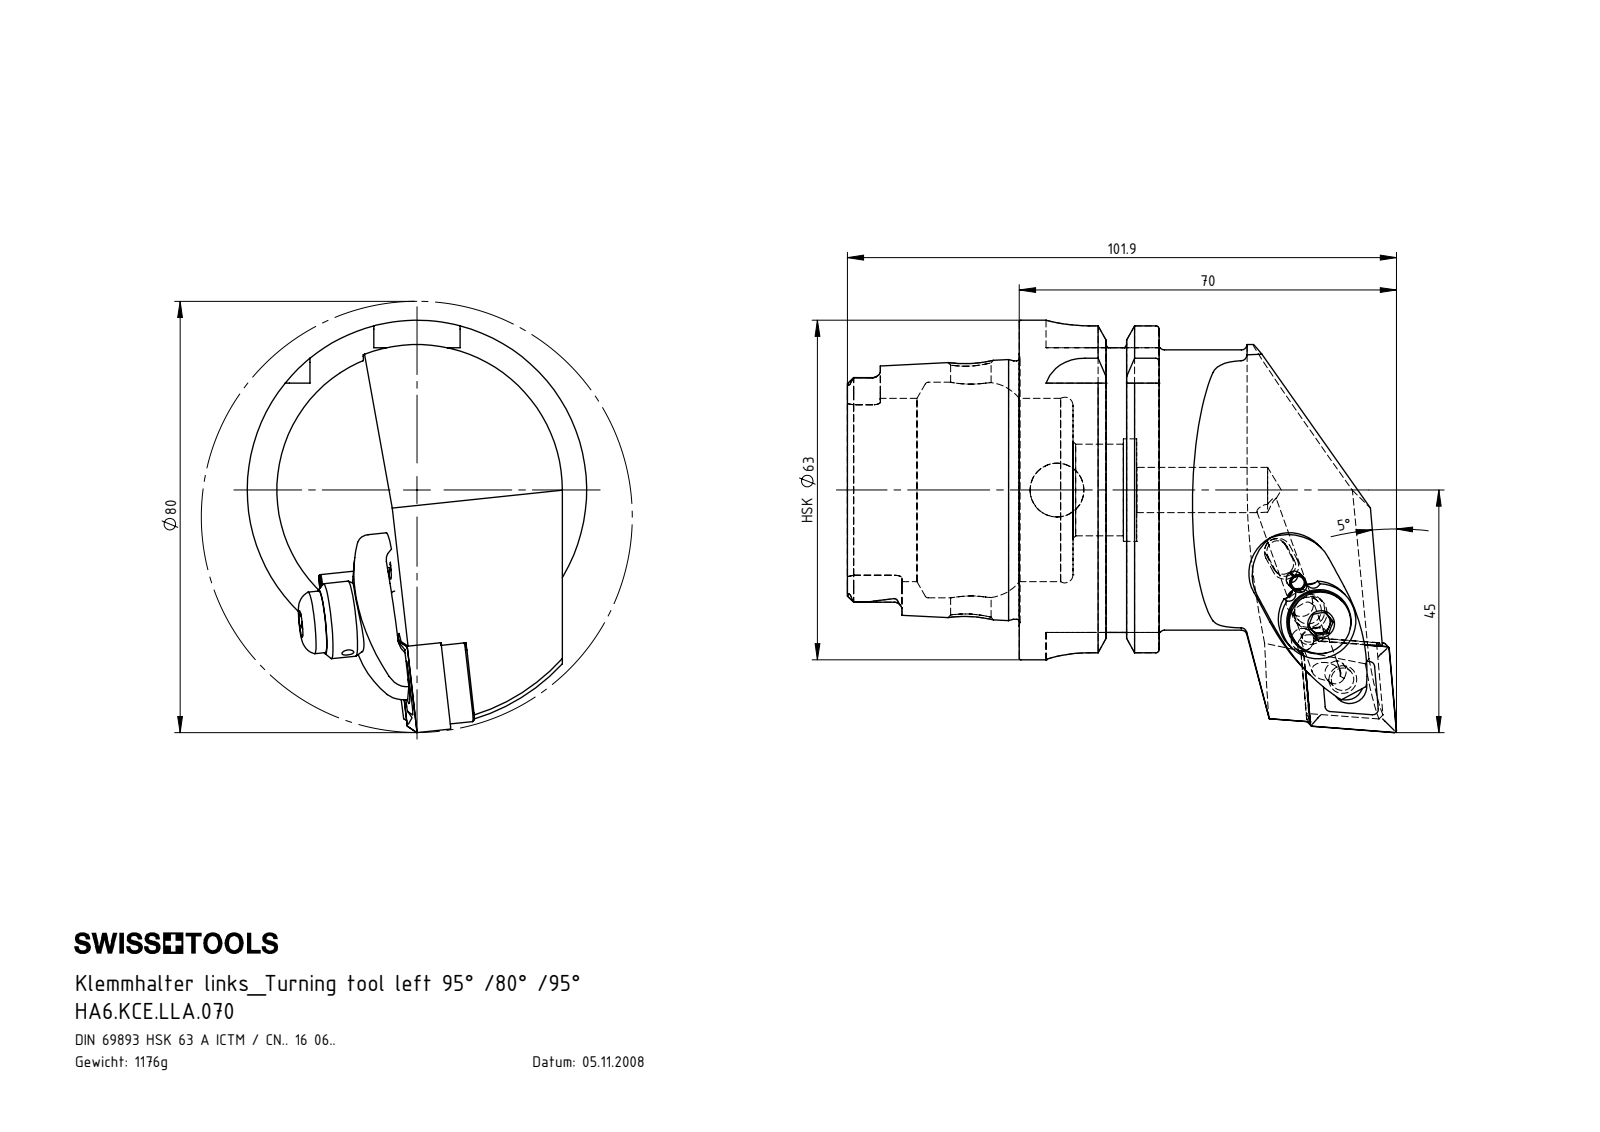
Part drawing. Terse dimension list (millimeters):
name: ISO 13337 - 3 x 12_PreviewCfg; HA6-KCE.LLA.070_C; WCC-ER5.102.012_B; WCE-ER2.001.012_A (+7 more)
written by: SolidWorks 2017 (AUTOMOTIVE_DESIGN)
unit: mm
bodies: 12 solids, 464 faces (125 planar, 150 cylindrical, 189 other)
size: 101.9 × 76.5 × 63
volume: 148 539 mm³; area: 36 454 mm²
holes: 3× ⌀2, 3× ⌀5, 2× ⌀4.2, 1× ⌀2.4, 1× ⌀3, 1× ⌀6, 1× ⌀6.2, 1× ⌀6.35, 1× ⌀7, 1× ⌀7.5, 1× ⌀7.9, 1× ⌀8.4
bosses: 2× ⌀6, 2× ⌀3, 1× ⌀63, 1× ⌀54.95, 1× ⌀52, 1× ⌀47.94, 1× ⌀14, 1× ⌀11.5
rounds: 6× R0.45, 6× R1.4, 4× R0.4, 4× R0.79, 4× R1, 4× R8, 3× R1.5, 2× R0.79
face distances: 25.95, 16, 9.95, 31.9, 41.85, 57.85, 52.8, 21.8, 4.76, 11.85
hole spacings: 8.2, 13.64, 23.41, 5.97, 6.15, 7.99, 8, 10.6
